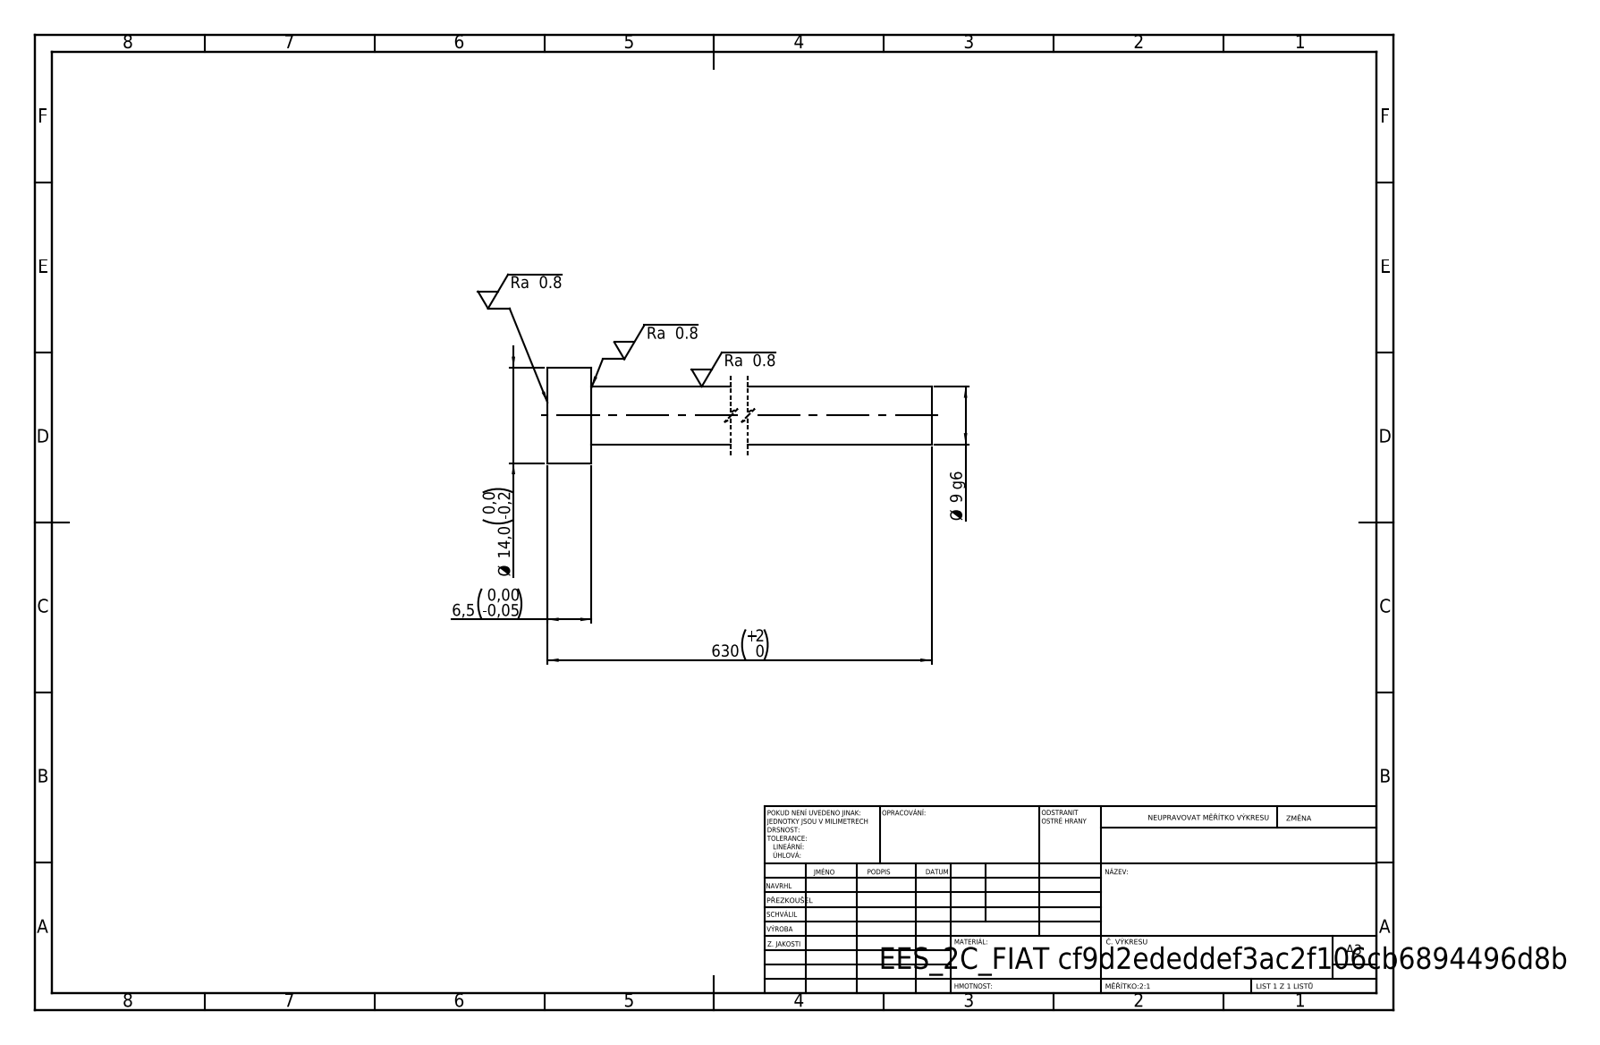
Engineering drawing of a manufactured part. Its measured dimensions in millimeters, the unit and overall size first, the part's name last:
Units: millimetres
Overall size (bounding box): 630 × 14 × 14
Round bosses / shafts (diameter × count): ⌀14 ×1, ⌀8.5 ×1
Main face-to-face distances: 6.5, 630, 623.5
Volume: 36 381 mm³ · Surface area: 17 243 mm²
Bodies: 1 solid, 7 faces (3 planar, 4 cylindrical, 0 other)
STEP written by: SolidWorks 2019 (CONFIG_CONTROL_DESIGN)
